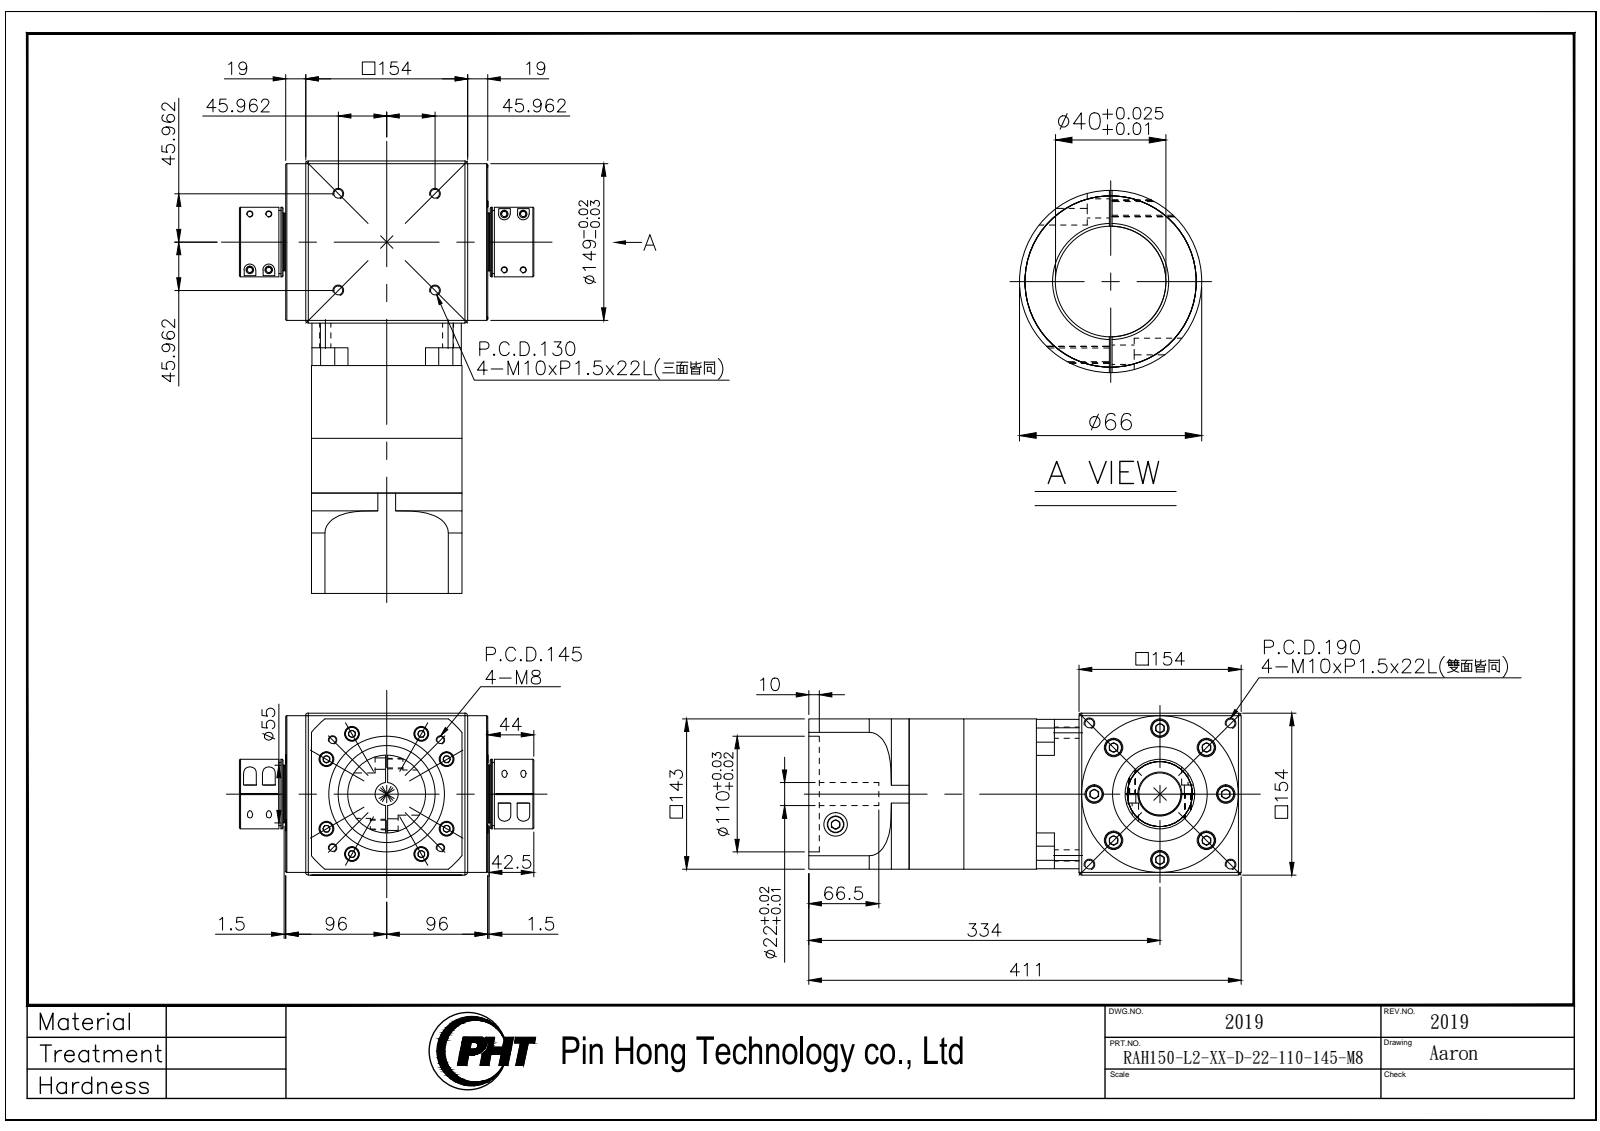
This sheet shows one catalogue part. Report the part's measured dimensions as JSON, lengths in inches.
{"part_name": "RAH150-L2-XX-D-22-110-145-M8_2019", "step_written_by": "SolidWorks 2016 (AUTOMOTIVE_DESIGN)", "units": "inches", "bodies": {"solids": 4, "faces": 1251, "planar": 633, "cylindrical": 400, "other": 218}, "overall_size": [16.181, 11.024, 6.063], "volume_in3": 511.4, "surface_area_in2": 920.3, "round_holes": [[0.335, 12], [0.354, 8], [0.433, 8], [0.551, 8], [0.689, 8], [0.276, 6], [0.268, 4], [0.413, 4], [0.886, 2], [0.866, 1], [1.575, 1], [1.732, 1]], "round_bosses_or_shafts": [[0.63, 12], [0.512, 8], [0.413, 8], [0.394, 8], [0.236, 8], [5.866, 1], [5.669, 1], [5.63, 1]], "partial_cylinders_radius": [[0.139, 8], [0.217, 8], [0.394, 4], [3.15, 1], [3.642, 1], [3.74, 1], [4.228, 1]], "face_to_face_distances": [6.063, 0.217, 5.846, 2.717, 4.311, 1.594, 7.657, 5.63, 10.374, 0.965], "hole_center_spacings": [2.598, 0.674, 0.756, 0.999, 1.883, 2.651, 3.14, 3.326]}
